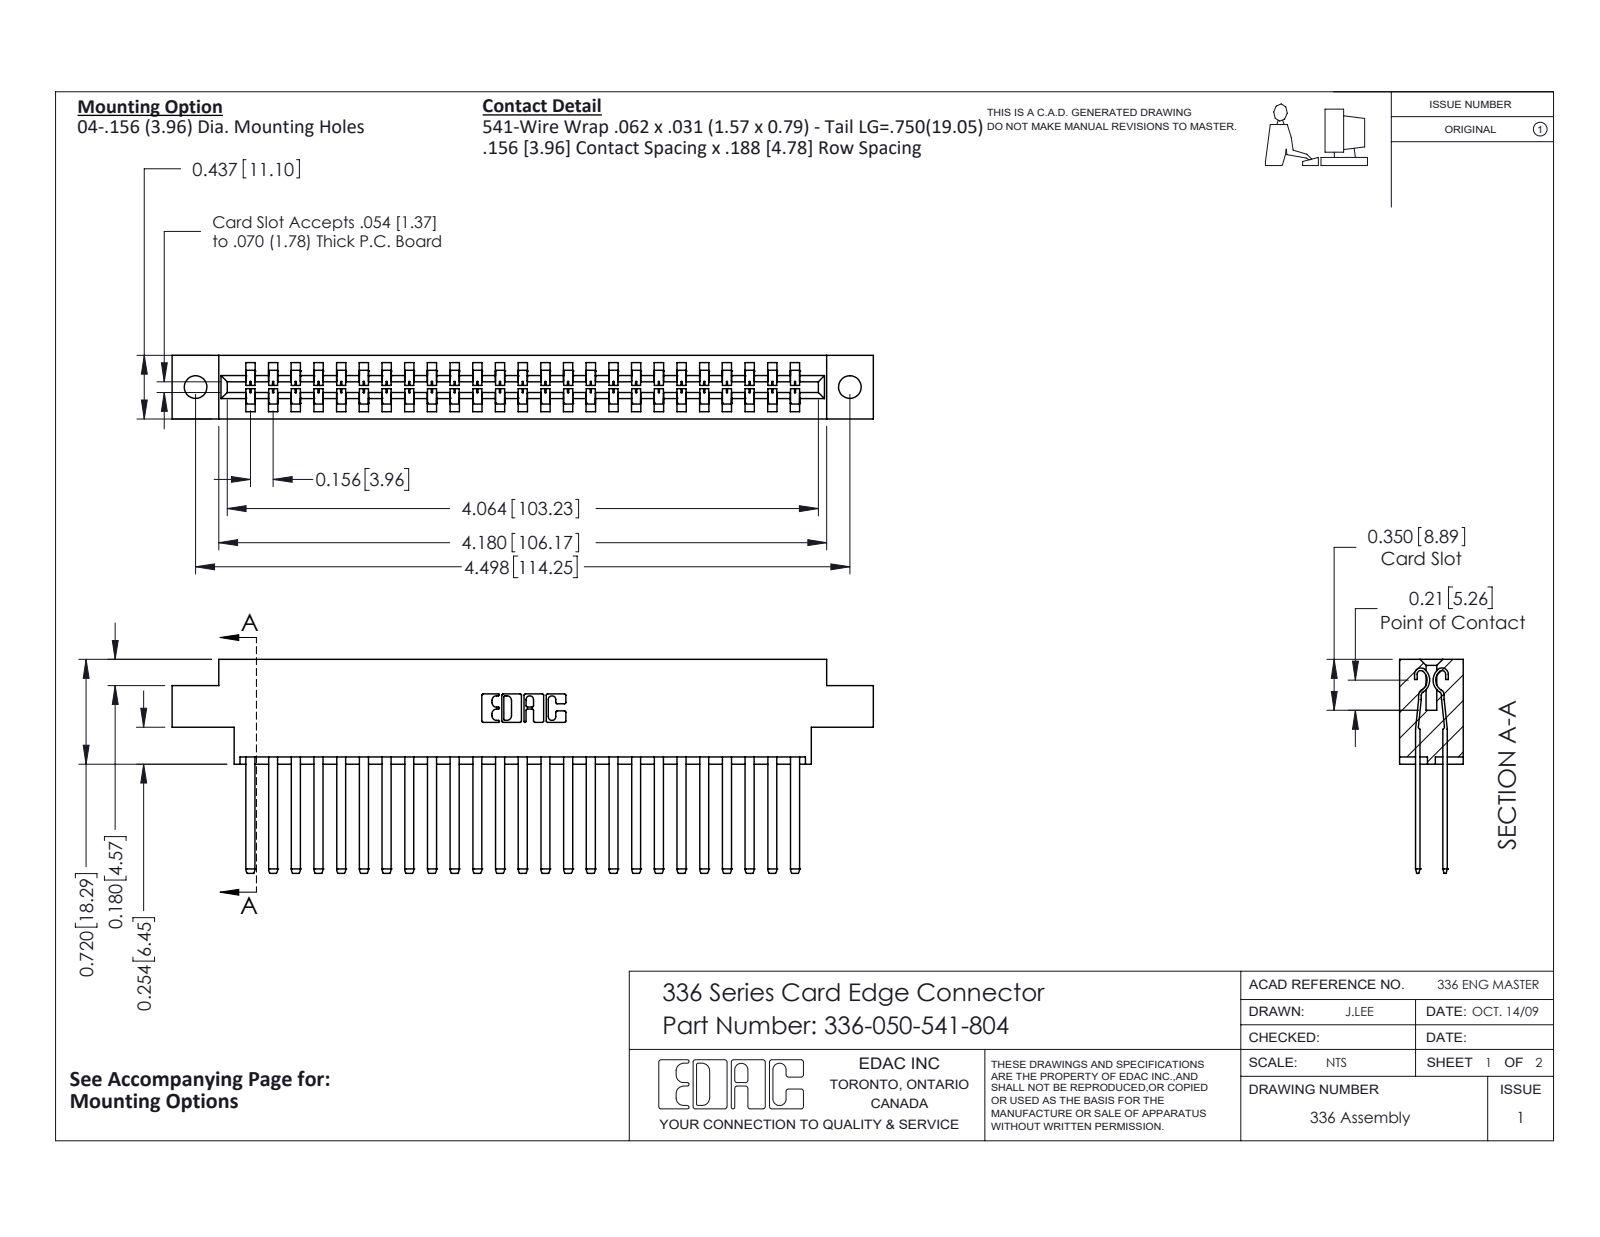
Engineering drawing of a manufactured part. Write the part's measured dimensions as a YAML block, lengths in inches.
part_name: "336-290-001_336-290-541; 336 Part_Offset - .156 Dia - TH; 336-050-541-804"
step_written_by: "SolidWorks 2020 (CONFIG_CONTROL_DESIGN)"
units: inches
bodies: {solids: 51, faces: 2218, planar: 1374, cylindrical: 844, other: 0}
overall_size: [4.821, 1.47, 0.437]
volume: 1.115
surface_area: 35.54
round_holes:
  - {diameter: 0.156, count: 2}
partial_cylinders:
  - {radius: 0.004, count: 100}
  - {radius: 0.056, count: 50}
  - {radius: 0.01, count: 22}
  - {radius: 0.007, count: 6}
  - {radius: 0.031, count: 6}
  - {radius: 0.022, count: 4}
  - {radius: 0.04, count: 4}
  - {radius: 0.026, count: 3}
face_to_face_distances: [0.188, 0.328, 0.14, 0.297, 0.109, 0.031, 0.437, 0.033, 0.181, 0.256]
hole_center_spacings: [4.498]
